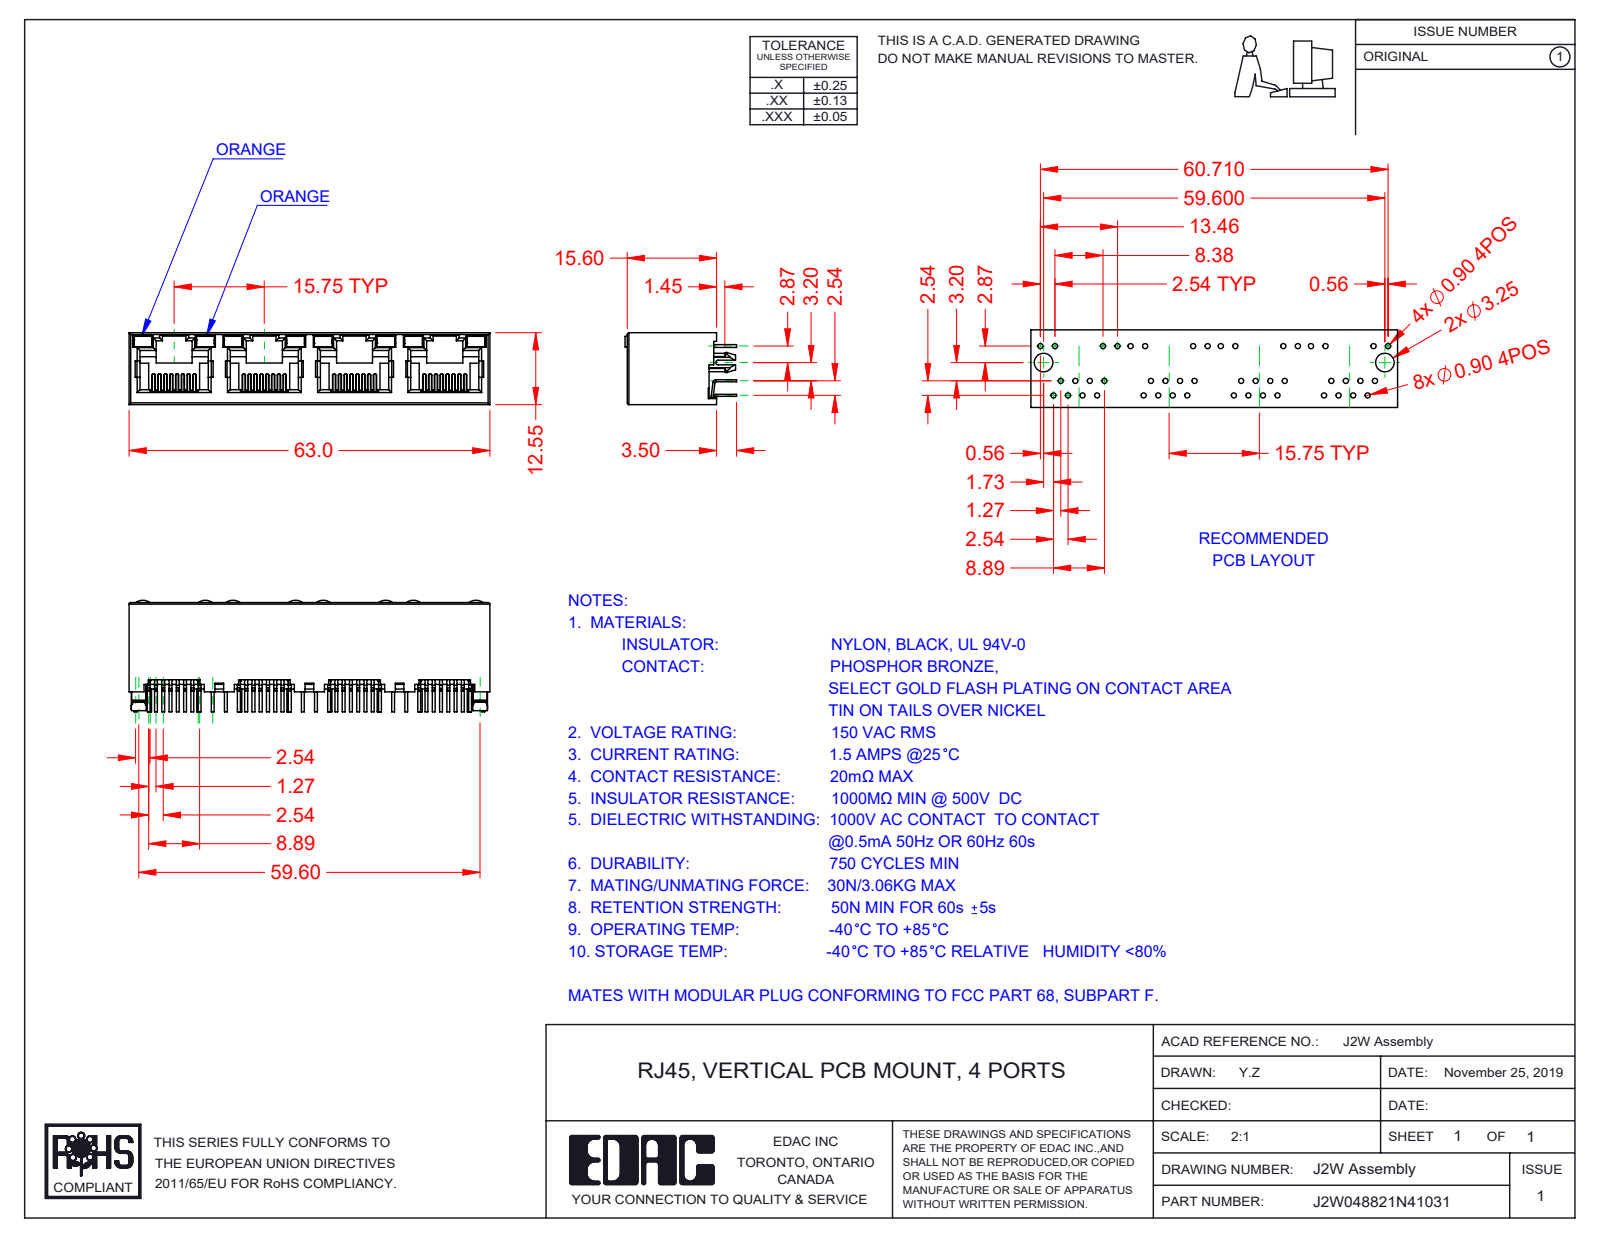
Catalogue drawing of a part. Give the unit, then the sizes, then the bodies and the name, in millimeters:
Units: millimetres
Overall size (bounding box): 63 × 19.5 × 12.55
Partial cylindrical surfaces — rounded edges, fillets, slot ends (radius × count): R0.15 ×64, R0.2 ×29, R0.5 ×28, R0.3 ×14, R0.45 ×8, R2 ×8, R0.25 ×2, R1.5 ×2
Main face-to-face distances: 12.55, 11.9, 0.65, 15.75, 0.36, 1.5, 0.78, 0.6, 11.3, 31.5
Volume: 5 335 mm³ · Surface area: 13 144 mm²
Bodies: 45 solids, 3135 faces (2600 planar, 477 cylindrical, 58 other)
Part name (STEP PRODUCT): 2W LED LH_4-Orange; 2W Contacts; J2W048821N44131; 2W Insulator (+2 more)
STEP written by: SolidWorks 2016 (CONFIG_CONTROL_DESIGN)
